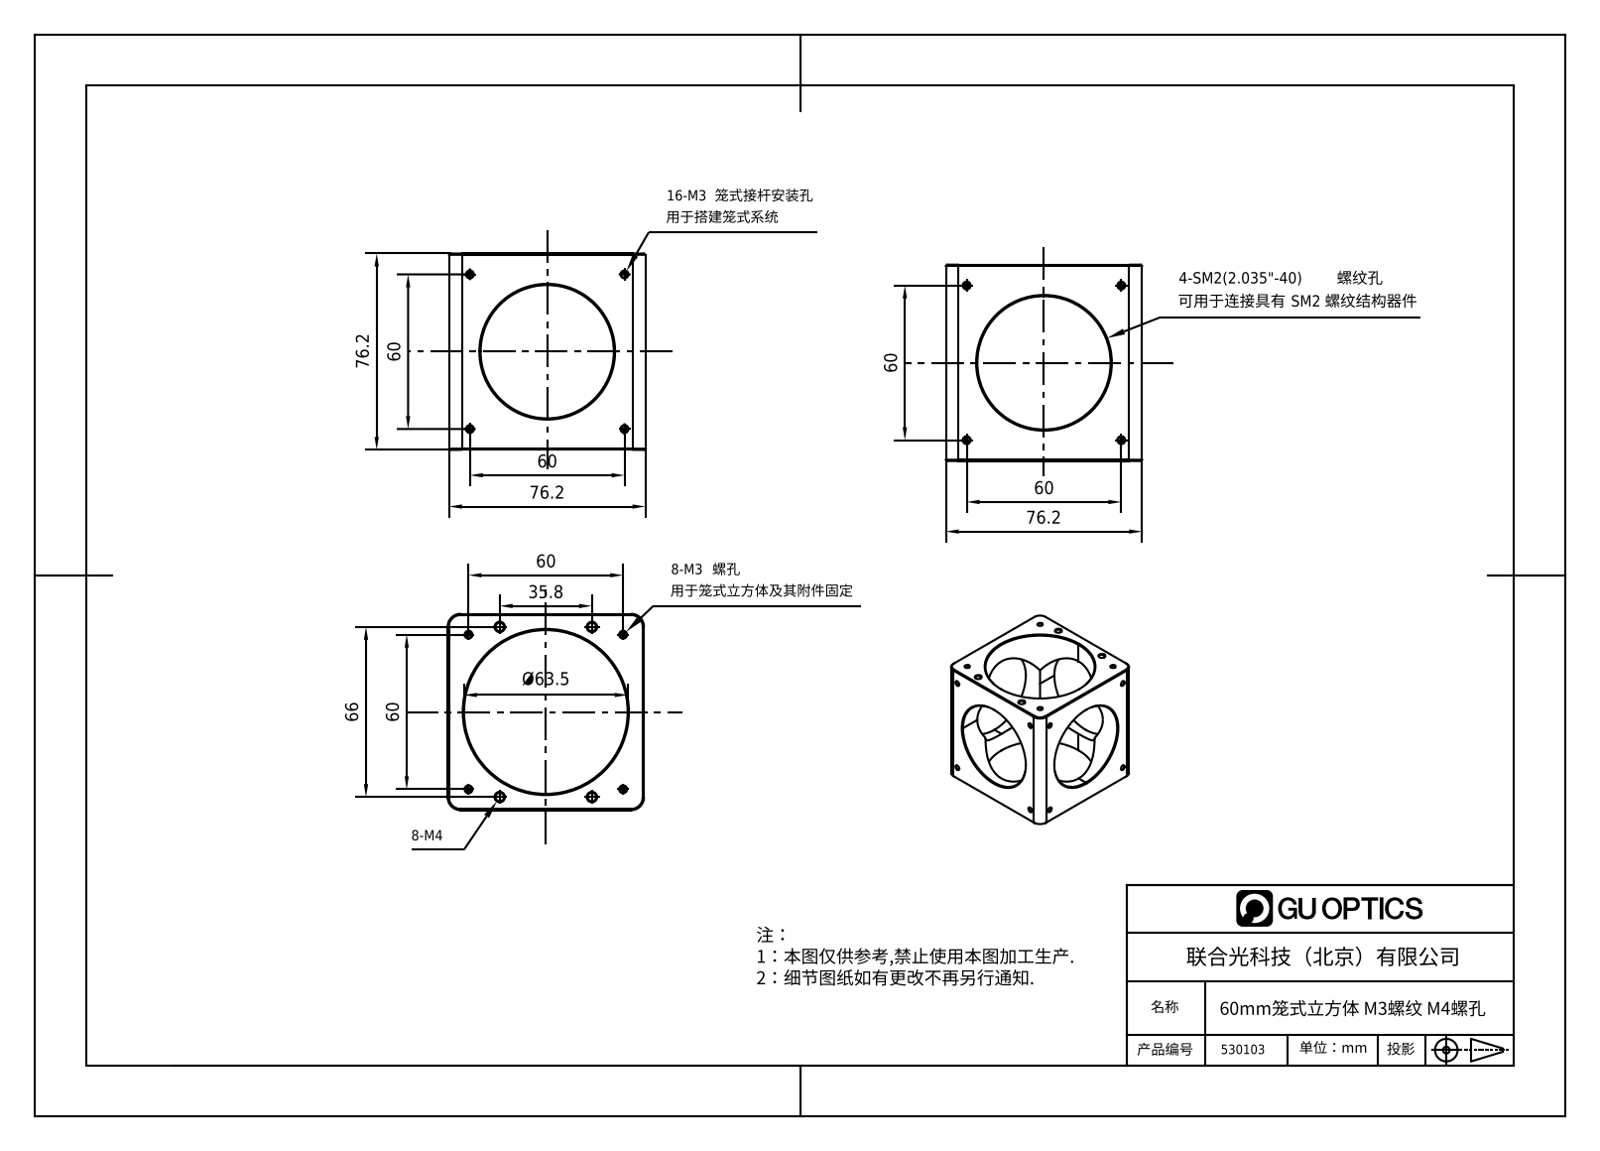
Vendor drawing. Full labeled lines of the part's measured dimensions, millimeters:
Part name (STEP PRODUCT): 2.3.7.4_L60F-BM_60 mm笼式立方体，带M3螺纹，M4螺孔
STEP written by: SolidWorks 2018 (CONFIG_CONTROL_DESIGN)
Units: millimetres
Bodies: 0 solids, 178 faces (14 planar, 80 cylindrical, 84 other)
Overall size (bounding box): 76.2 × 76.2 × 76.2
Round holes (diameter × count): ⌀2.5 ×12, ⌀3.3 ×4, ⌀51.69 ×2, ⌀63.5 ×1
Partial cylindrical surfaces — rounded edges, fillets, slot ends (radius × count): R5 ×4
Main face-to-face distances: 76.2, 107.04
Hole centre spacings: 42.43, 60, 84.85, 12.47, 37.54, 47.99, 64.15, 79.14
